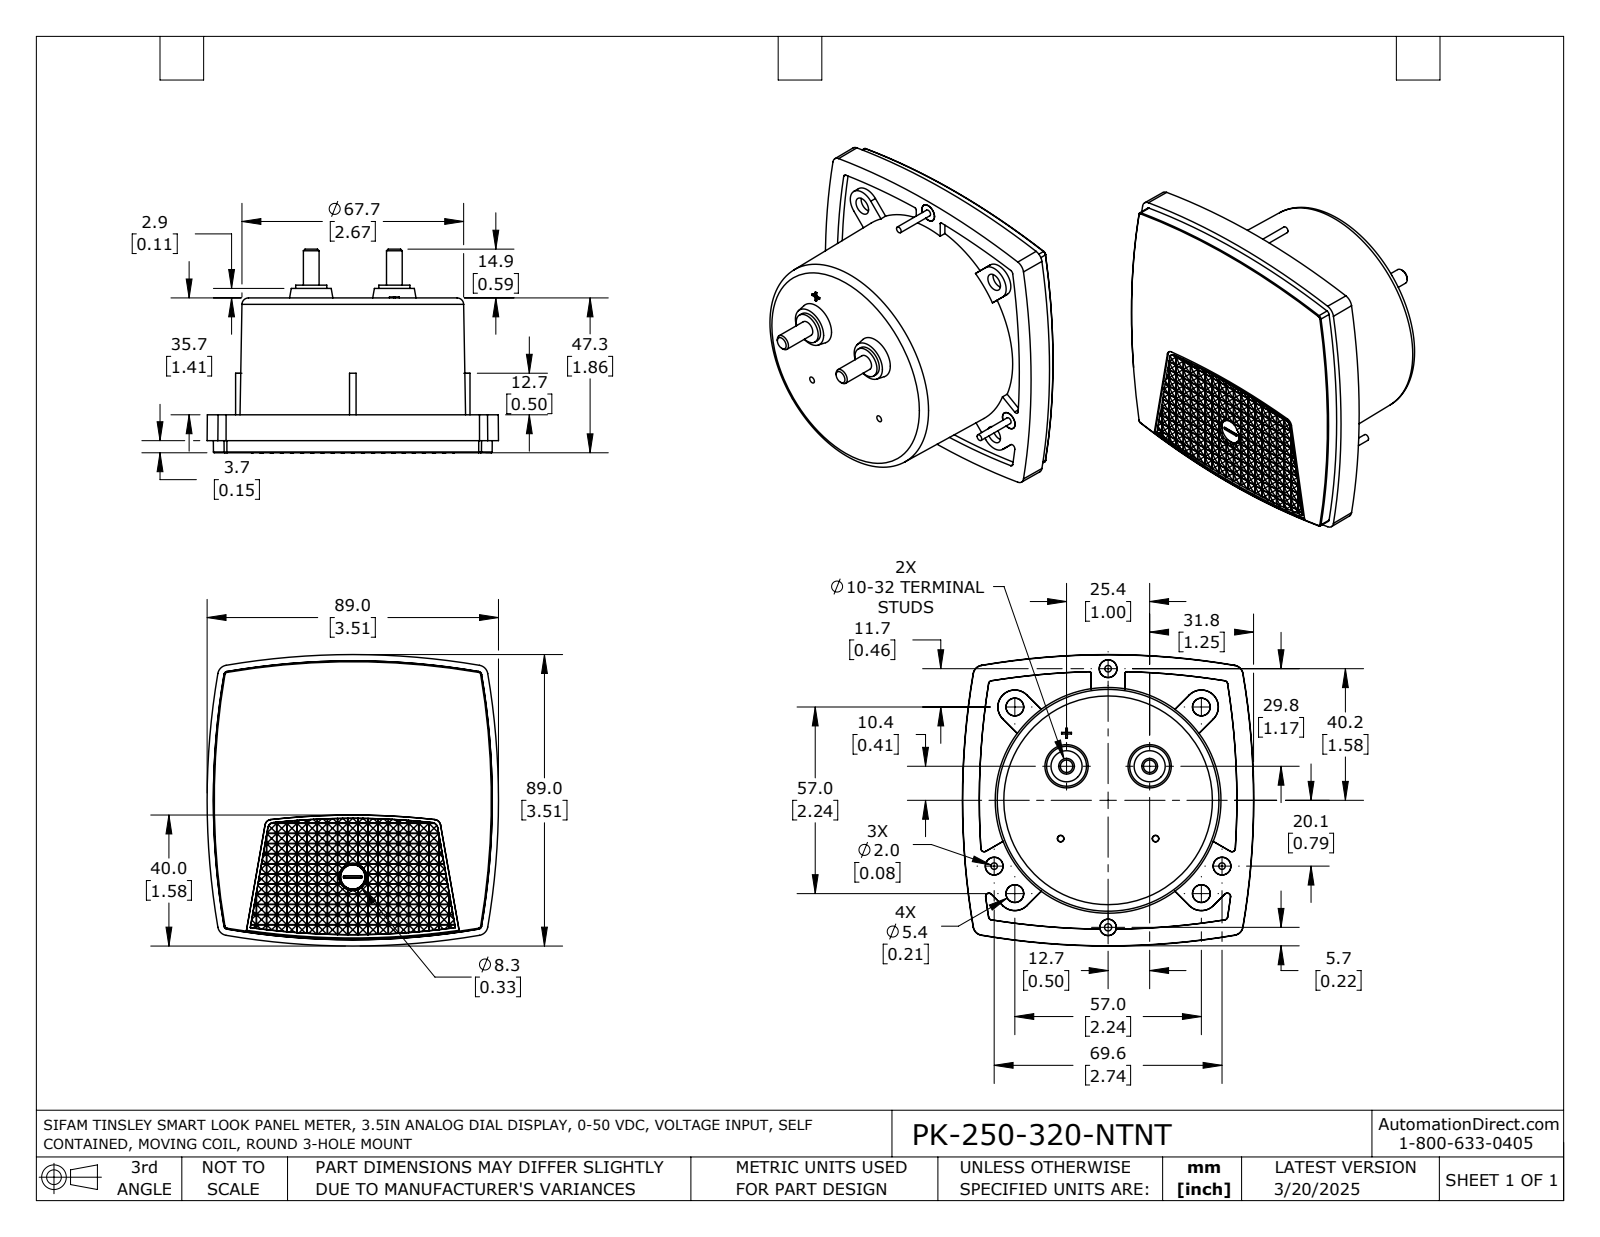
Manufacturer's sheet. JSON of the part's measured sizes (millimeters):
{"part_name": "PK-250-320-NTNT", "step_written_by": "SolidWorks 2021 (AUTOMOTIVE_DESIGN)", "units": "millimeters", "bodies": {"solids": 1, "faces": 1078, "planar": 950, "cylindrical": 23, "other": 105}, "overall_size": [89, 89, 62.3], "volume_mm3": 212900, "surface_area_mm2": 28570, "round_holes": [[2.2, 1]], "round_bosses_or_shafts": [[5.4, 3], [2, 3], [9.5, 2], [4.8, 2]], "partial_cylinders_radius": [[227.6, 1]], "face_to_face_distances": [47.3, 35.7, 11.6, 2, 37.7, 9.6, 0.6, 2.4, 1.8, 3]}
